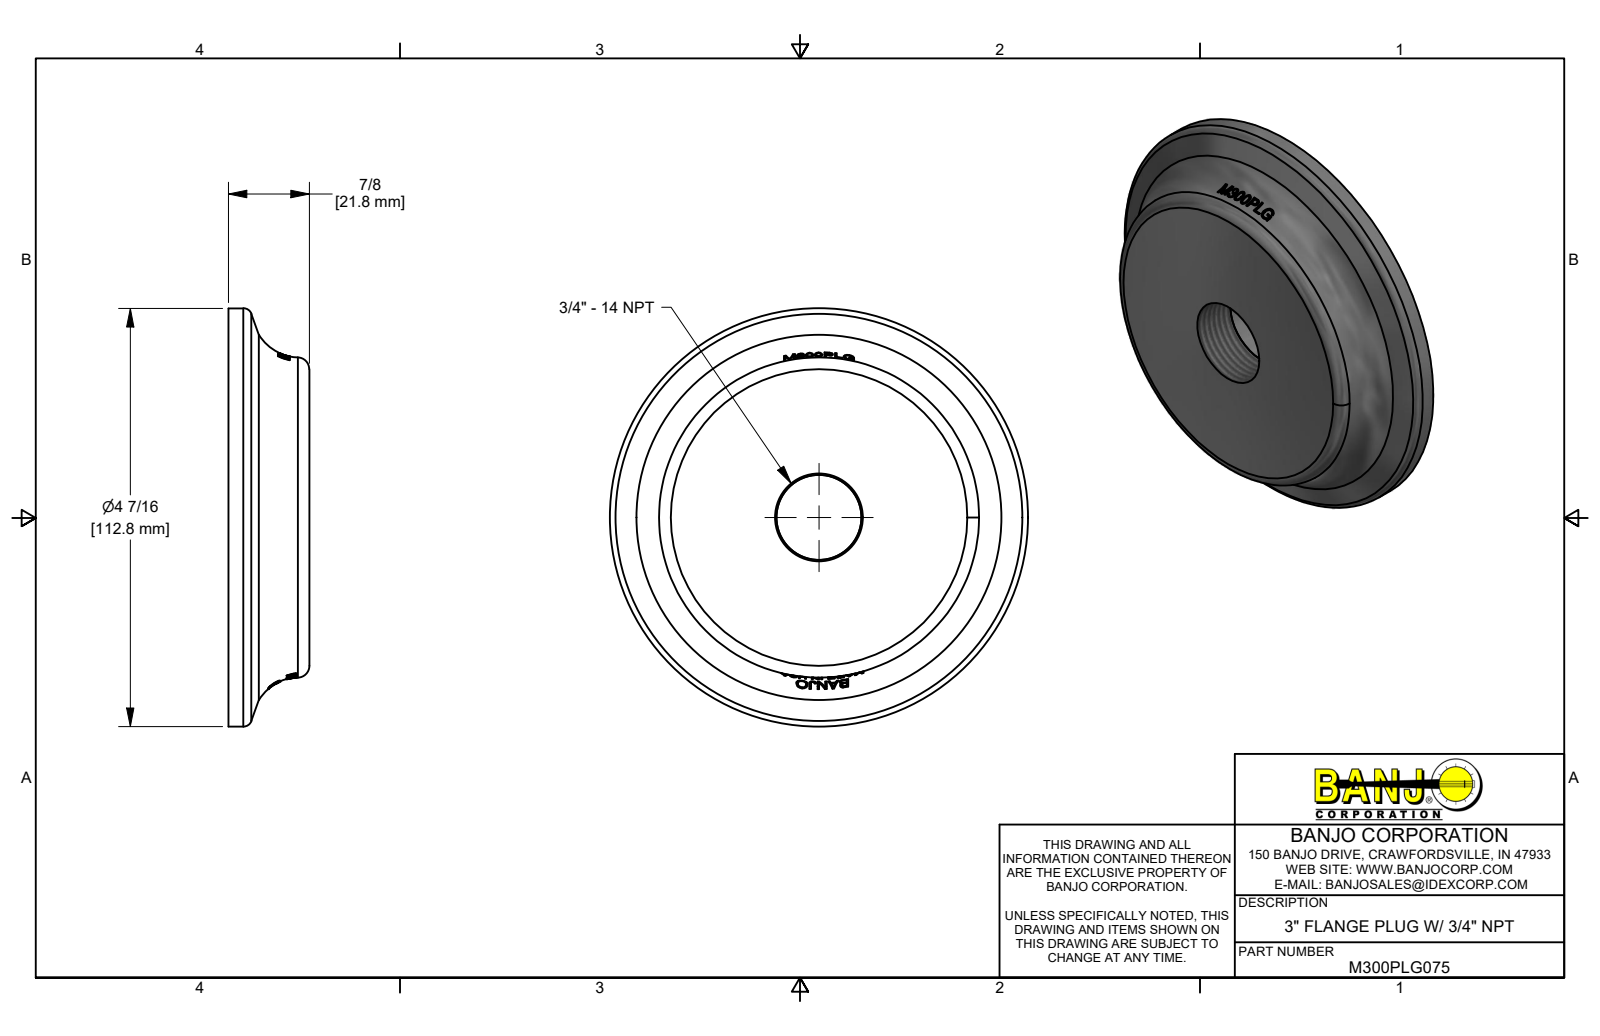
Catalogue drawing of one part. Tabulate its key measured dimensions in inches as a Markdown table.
| quantity | value |
| --- | --- |
| part name | M300PLG075; M300PLG075X |
| STEP written by | Autodesk Inventor 2019 (AUTOMOTIVE_DESIGN) |
| units | inches |
| bodies | 1 solid, 313 faces (156 planar, 5 cylindrical, 152 other) |
| overall size | 4.44 × 4.44 × 0.86 |
| volume | 6.821 in³ |
| surface area | 44.16 in² |
| round holes (diameter × count) | 0.9 × 1, 3 × 1, 3.75 × 1 |
| round bosses / shafts (diameter × count) | 4.44 × 1, 1.8 × 1 |
| main face-to-face distances | 0.86, 0.1, 0.76, 0.45, 0.35, 0.41, 0.11, 0.34, 0.75, 0.016 |
